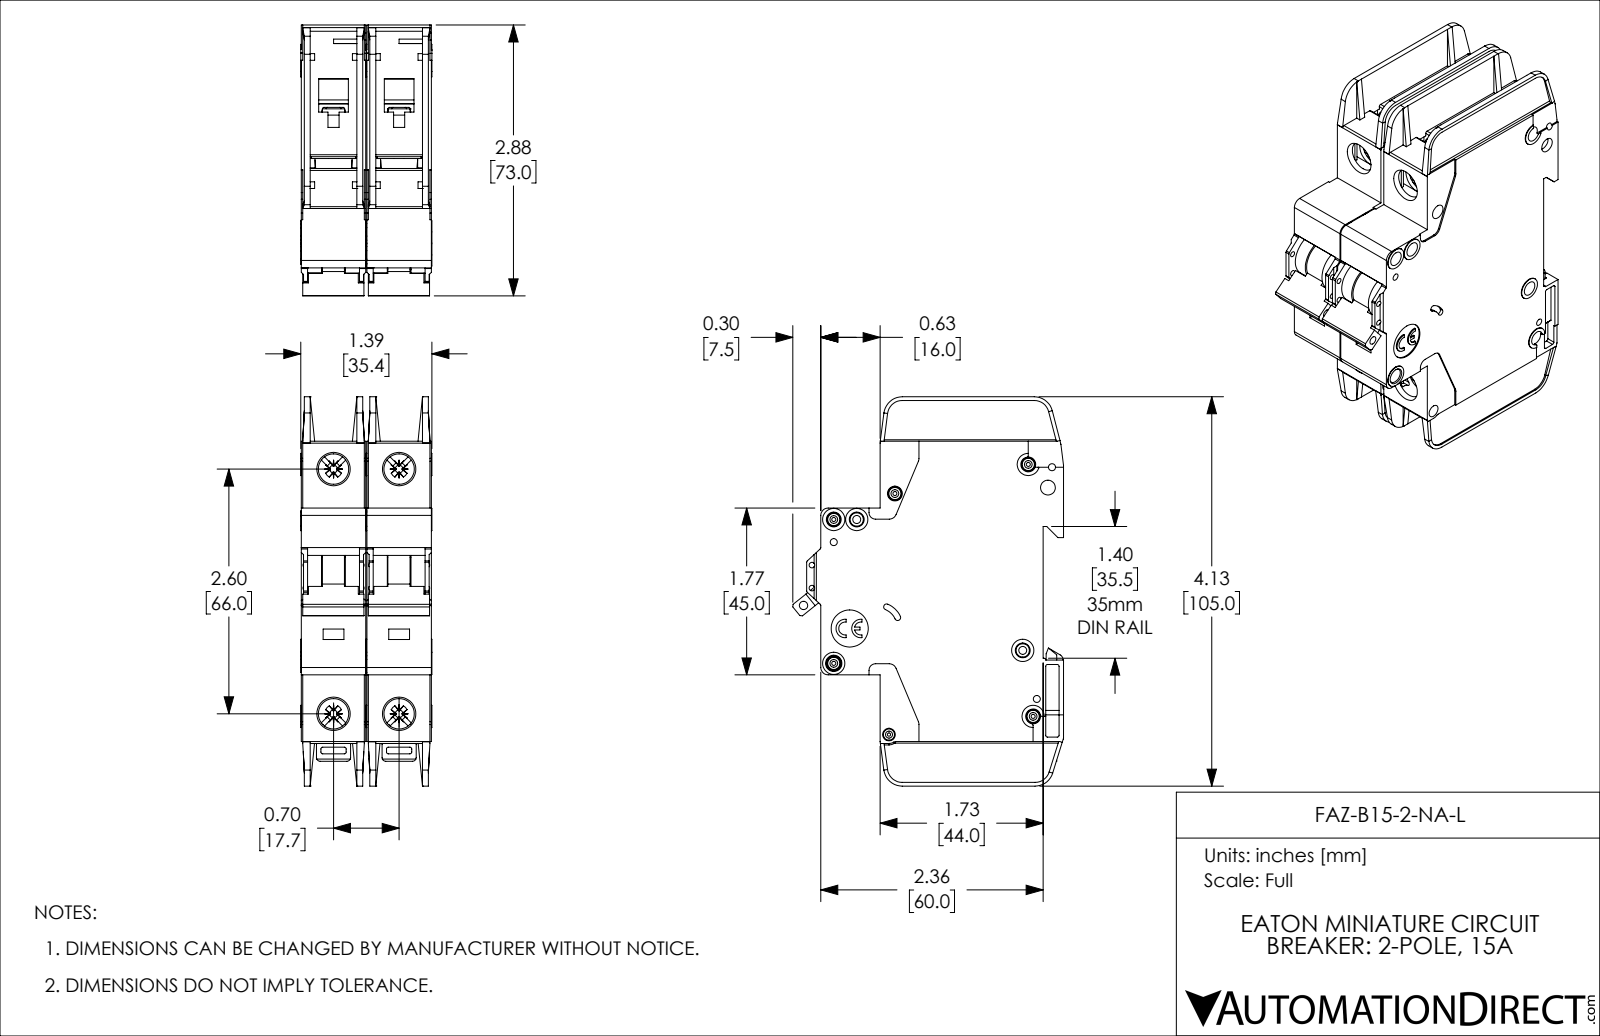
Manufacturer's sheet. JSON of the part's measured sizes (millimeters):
{"part_name": "FAZ-B15-2-NA-L", "step_written_by": "SolidWorks 2019 (AUTOMOTIVE_DESIGN)", "units": "millimeters", "bodies": {"solids": 2, "faces": 2254, "planar": 1342, "cylindrical": 714, "other": 198}, "overall_size": [105, 73.1, 35.4], "volume_mm3": 153500, "surface_area_mm2": 52910, "round_holes": [[4, 8], [1.1, 5], [1.9, 4], [8.2, 4], [1.5, 2], [2.2, 2], [0.9, 1], [2.3, 1], [2.5, 1], [3.4, 1], [10, 1]], "round_bosses_or_shafts": [[3.3, 5], [6, 4], [3, 3], [2.5, 2]], "partial_cylinders_radius": [[0.5, 57], [0.4, 20], [1, 14], [2, 10], [1.1, 8], [0.2, 5], [5, 5], [0.3, 4]], "face_to_face_distances": [17.7, 1.2, 17.4, 15, 2.4, 16.2, 13.8, 35.1, 18.9, 16.5], "hole_center_spacings": [6.2, 13.6, 17.7, 22.1, 66, 68.3, 4.8, 5.1]}
